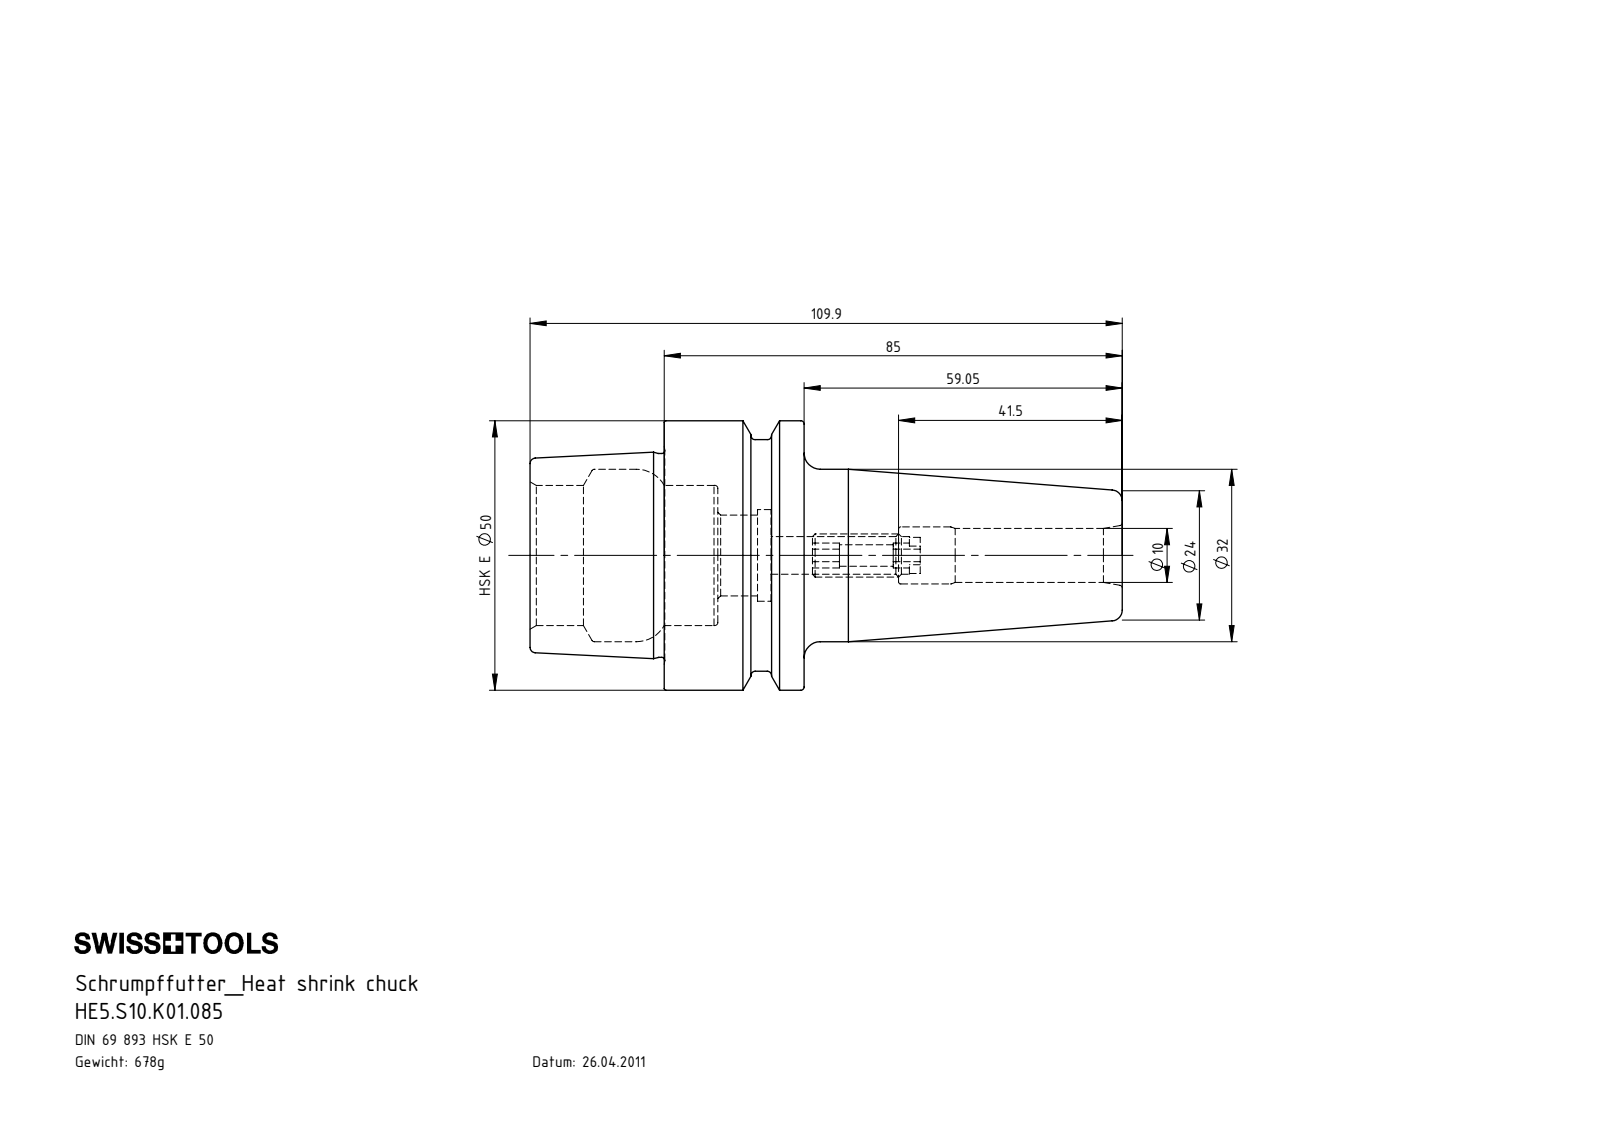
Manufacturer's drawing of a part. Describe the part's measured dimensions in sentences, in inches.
The part is named "HE5-S10.K01.085; ERU-AN3.K01.020_A; HE5-S10.K01.085_B_Fertigbearbeitung". Its 3-D file was written by "SolidWorks 2012 (AUTOMOTIVE_DESIGN)". It is 2 solids with 133 faces: 43 planar, 32 cylindrical and 58 other. Overall it measures 4.327 by 1.969 by 1.969 inches. Its volume is 5.269 cubic inches and its surface area 34.69 square inches. Round holes: 1 of diameter 0.157, 1 of diameter 0.276, 1 of diameter 0.394, 1 of diameter 0.417, 1 of diameter 0.591, 1 of diameter 0.669, 1 of diameter 1.024, 1 of diameter 1.26. Round bosses or shafts: 1 of diameter 1.969, 1 of diameter 1.691, 1 of diameter 1.489, 1 of diameter 0.315. The main face-to-face distances are 1.022, 0.98, 2.002, 0.63, 1.372, 0.392, 4.327, 3.346, 2.955, 2.325.
